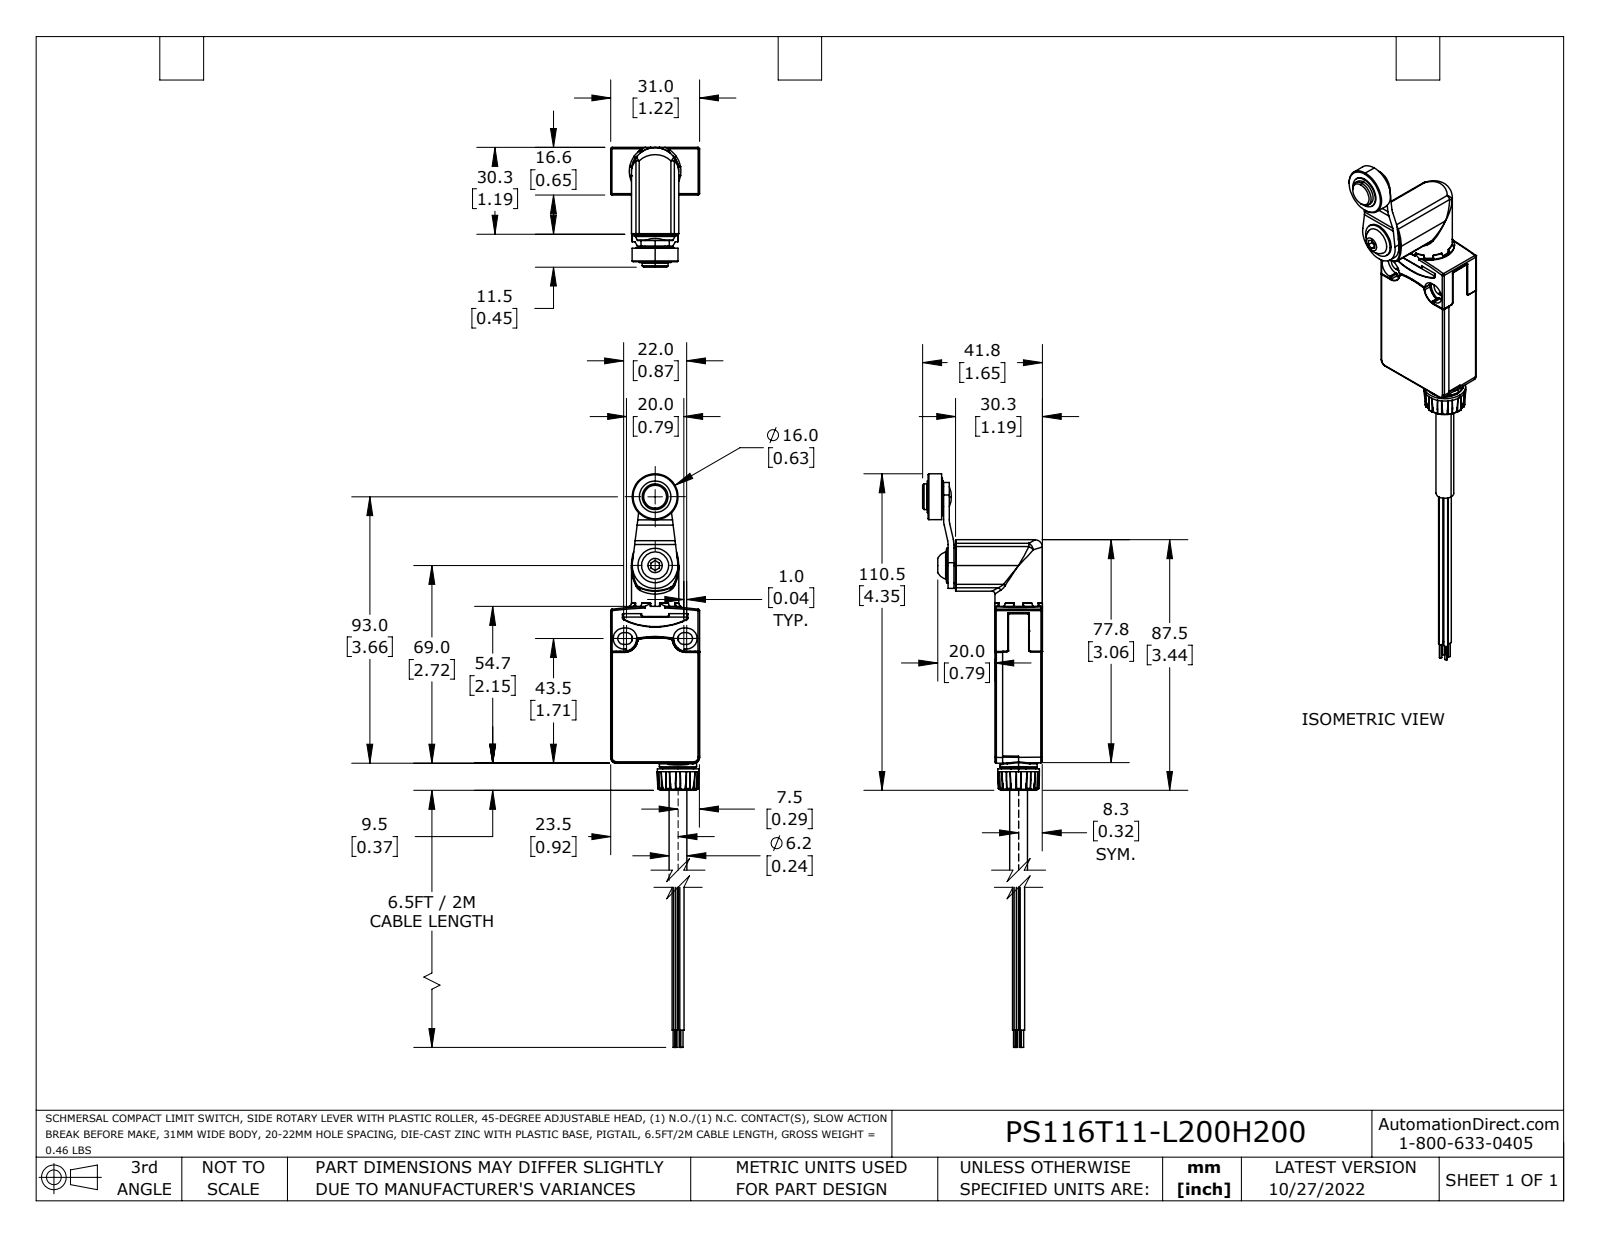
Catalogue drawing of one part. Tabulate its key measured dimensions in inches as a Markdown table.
| quantity | value |
| --- | --- |
| part name | PS116T11-L200H200_Default |
| STEP written by | SolidWorks 2021 (CONFIG_CONTROL_DESIGN) |
| units | inches |
| bodies | 1 solid, 1082 faces (335 planar, 442 cylindrical, 305 other) |
| overall size | 8.602 × 1.646 × 1.22 |
| volume | 2.425 in³ |
| surface area | 27.85 in² |
| round holes (diameter × count) | 0.48 × 2, 0.079 × 1, 0.252 × 1, 0.571 × 1, 0.583 × 1 |
| round bosses / shafts (diameter × count) | 0.059 × 4, 0.031 × 4, 0.512 × 2, 0.65 × 1, 0.63 × 1, 0.571 × 1, 0.567 × 1, 0.524 × 1 |
| partial cylindrical surfaces (radius × count) | 0.008 × 134, 0.004 × 61, 0.02 × 30, 0.014 × 10, 0.039 × 8, 0.012 × 6, 0.079 × 5, 0.081 × 4 |
| main face-to-face distances | 0.65, 0.652, 0.079, 1.22, 0.063, 0.118, 0.654, 0.016, 0.453, 0.291 |
| hole center spacings | 0.315 |
